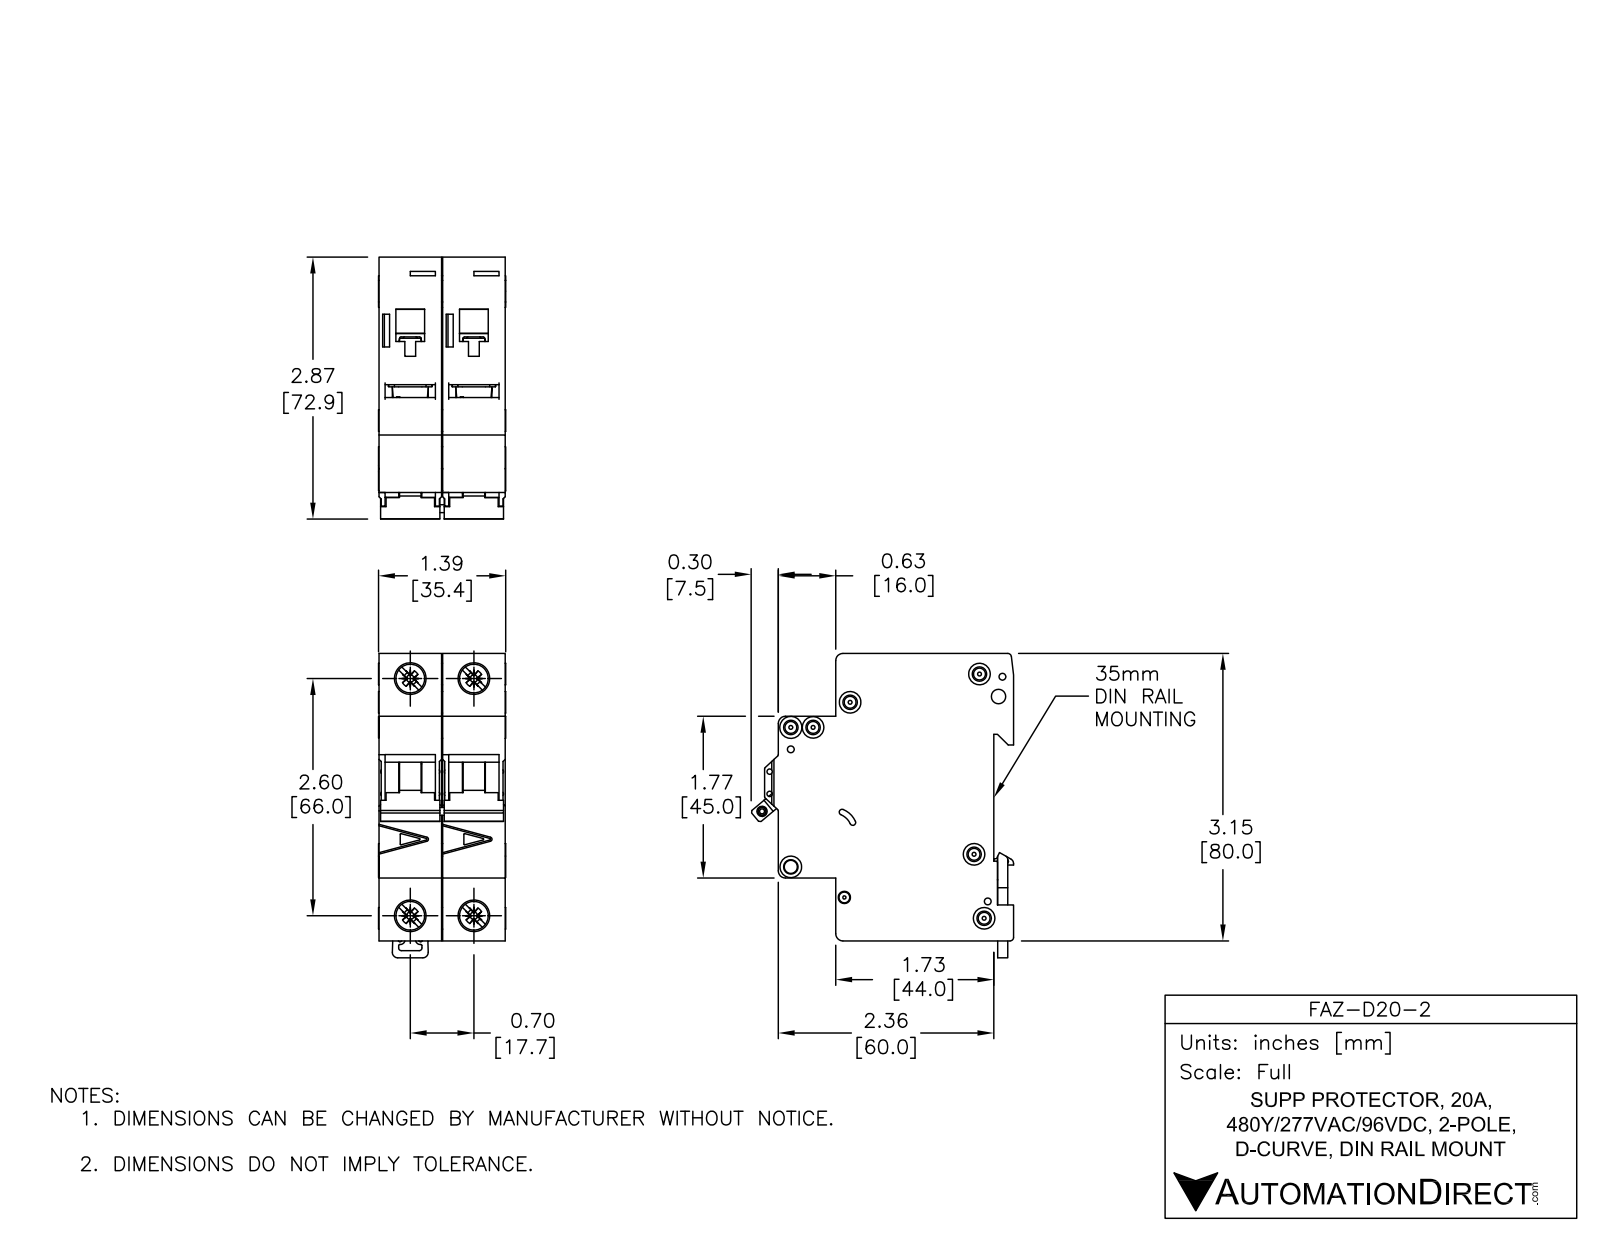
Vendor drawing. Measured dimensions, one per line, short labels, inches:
name: FAZ-D20-2
written by: SolidWorks 2014 (AUTOMOTIVE_DESIGN)
unit: in
bodies: 8 solids, 1104 faces (466 planar, 396 cylindrical, 242 other)
size: 3.338 × 2.876 × 1.394
volume: 9.142 in³; area: 60.14 in²
holes: 6× ⌀0.142, 3× ⌀0.075, 2× ⌀0.043, 2× ⌀0.059, 2× ⌀0.157, 2× ⌀0.281, 2× ⌀0.323, 1× ⌀0.085, 1× ⌀0.087, 1× ⌀0.1, 1× ⌀0.13, 1× ⌀0.134
bosses: 4× ⌀0.236, 2× ⌀0.323, 2× ⌀0.098
rounds: 49× R0.01, 19× R0.02, 10× R0.079, 8× R0.008, 8× R0.039, 2× R0.031, 2× R0.071, 2× R0.118
face distances: 0.697, 0.689, 1.386, 3.129, 0.217, 1.949, 1.732, 2.579, 2.362, 0.63
hole spacings: 0.244, 0.537, 0.697, 2.598, 2.69, 0.189, 0.204, 0.221
